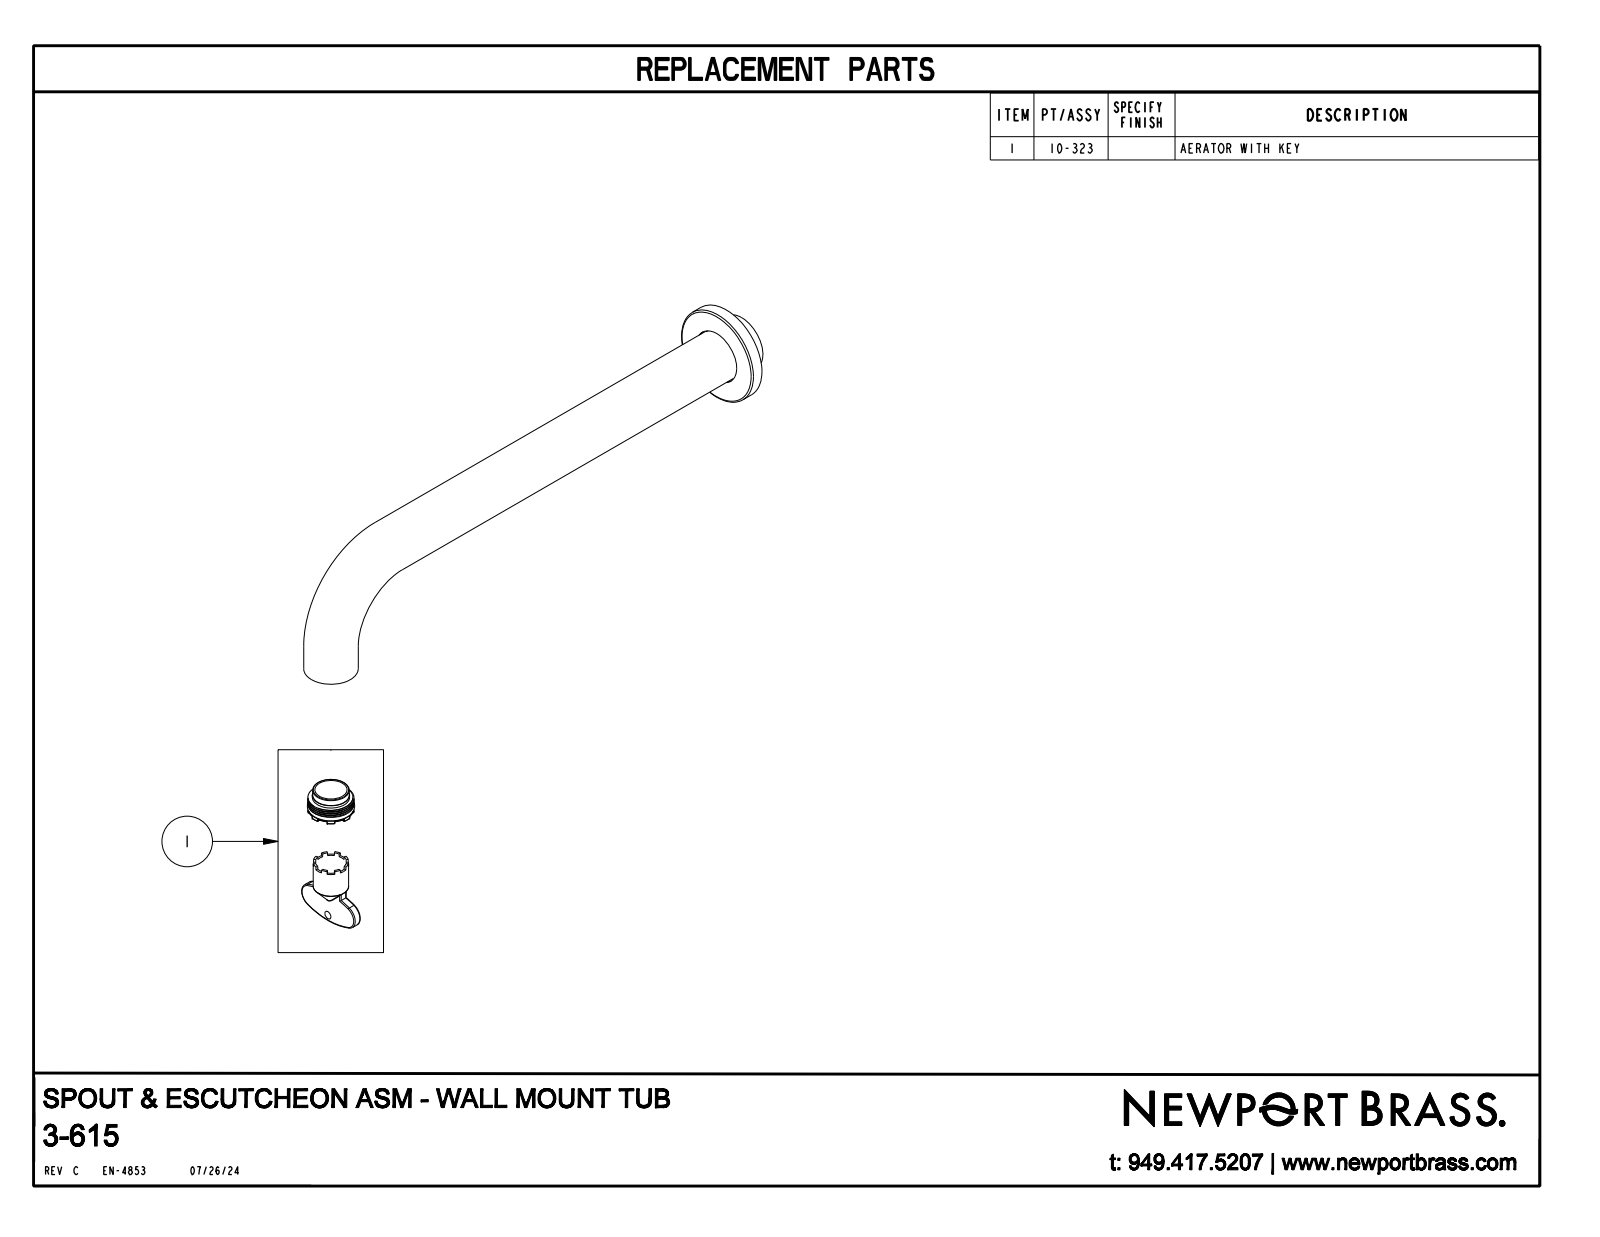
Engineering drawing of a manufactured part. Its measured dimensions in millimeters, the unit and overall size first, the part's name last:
Units: millimetres
Overall size (bounding box): 283.2 × 74.3 × 47
Round bosses / shafts (diameter × count): ⌀25.4 ×2, ⌀47 ×1, ⌀27.9 ×1
Main face-to-face distances: 6.4, 10.2, 16.5
Volume: 163 400 mm³ · Surface area: 28 260 mm²
Bodies: 1 solid, 16 faces (4 planar, 8 cylindrical, 4 other)
Part name (STEP PRODUCT): 3-615
STEP written by: CREO PARAMETRIC BY PTC INC, 2018400 (AUTOMOTIVE_DESIGN)
